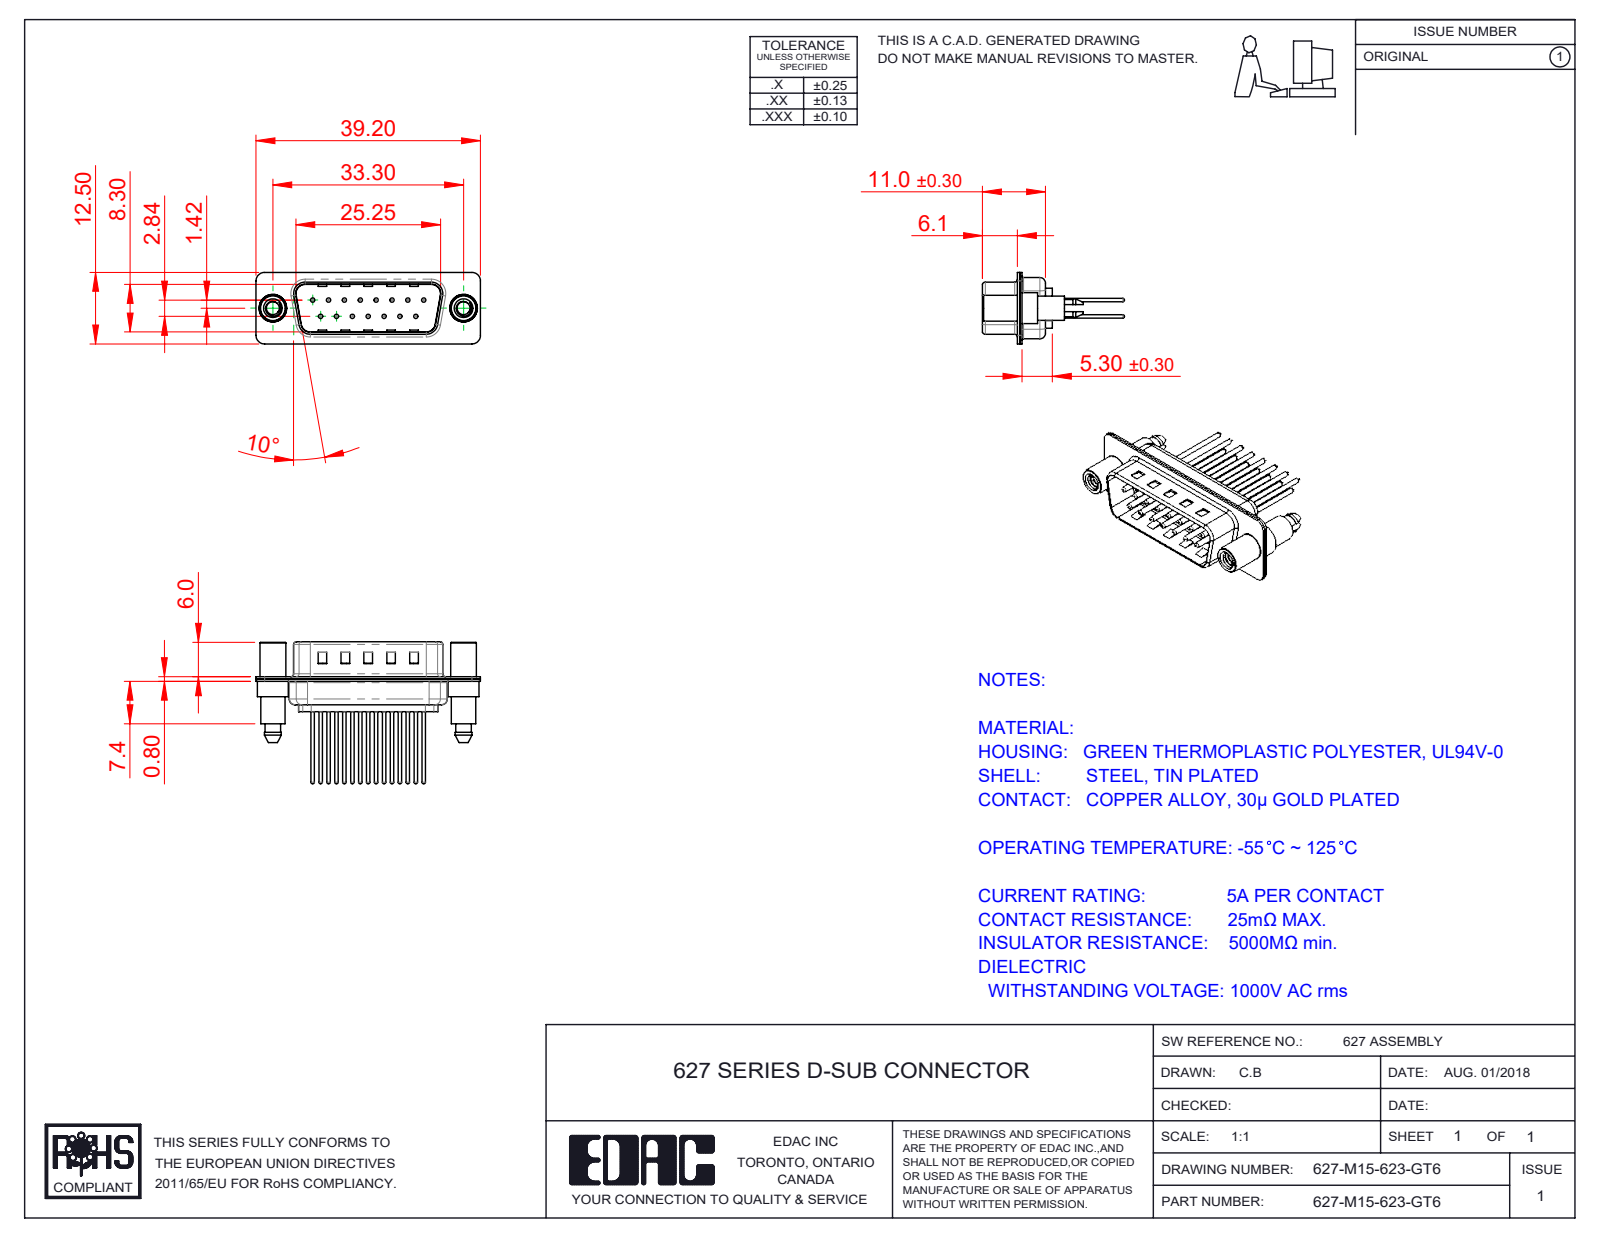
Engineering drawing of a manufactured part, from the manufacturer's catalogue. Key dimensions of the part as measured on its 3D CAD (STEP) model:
Part name (STEP PRODUCT): 627M Shell Front_15 Contacts; 627M Contact Row 1_23; 627M 4-40 Threaded Standoff and Boardlock; 627-M15-623-GT6 (+3 more)
STEP written by: SolidWorks 2020 (CONFIG_CONTROL_DESIGN)
Units: millimetres
Bodies: 20 solids, 947 faces (262 planar, 371 cylindrical, 314 other)
Overall size (bounding box): 39.2 × 24.77 × 12.5
Volume: 2 211 mm³ · Surface area: 5 471 mm²
Round holes (diameter × count): ⌀0.75 ×15, ⌀1.6 ×15, ⌀2 ×15, ⌀2.26 ×2, ⌀4 ×2, ⌀4.8 ×2
Round bosses / shafts (diameter × count): ⌀1.5 ×15, ⌀0.6 ×15, ⌀5.4 ×2, ⌀4.9 ×2, ⌀4.5 ×2, ⌀4.25 ×2
Partial cylindrical surfaces — rounded edges, fillets, slot ends (radius × count): R1.5 ×18, R2 ×12, R1.6 ×10, R0.5 ×8, R0.25 ×4, R0.6 ×4, R0.65 ×4, R0.9 ×4
Main face-to-face distances: 0.4, 0.8, 9.5, 9.1, 8.7, 9.9, 5.3, 1.2, 6.1, 5.7
Hole centre spacings: 3.16, 2.77, 5.54, 8.31, 11.08, 5.03, 5.04, 7.48
